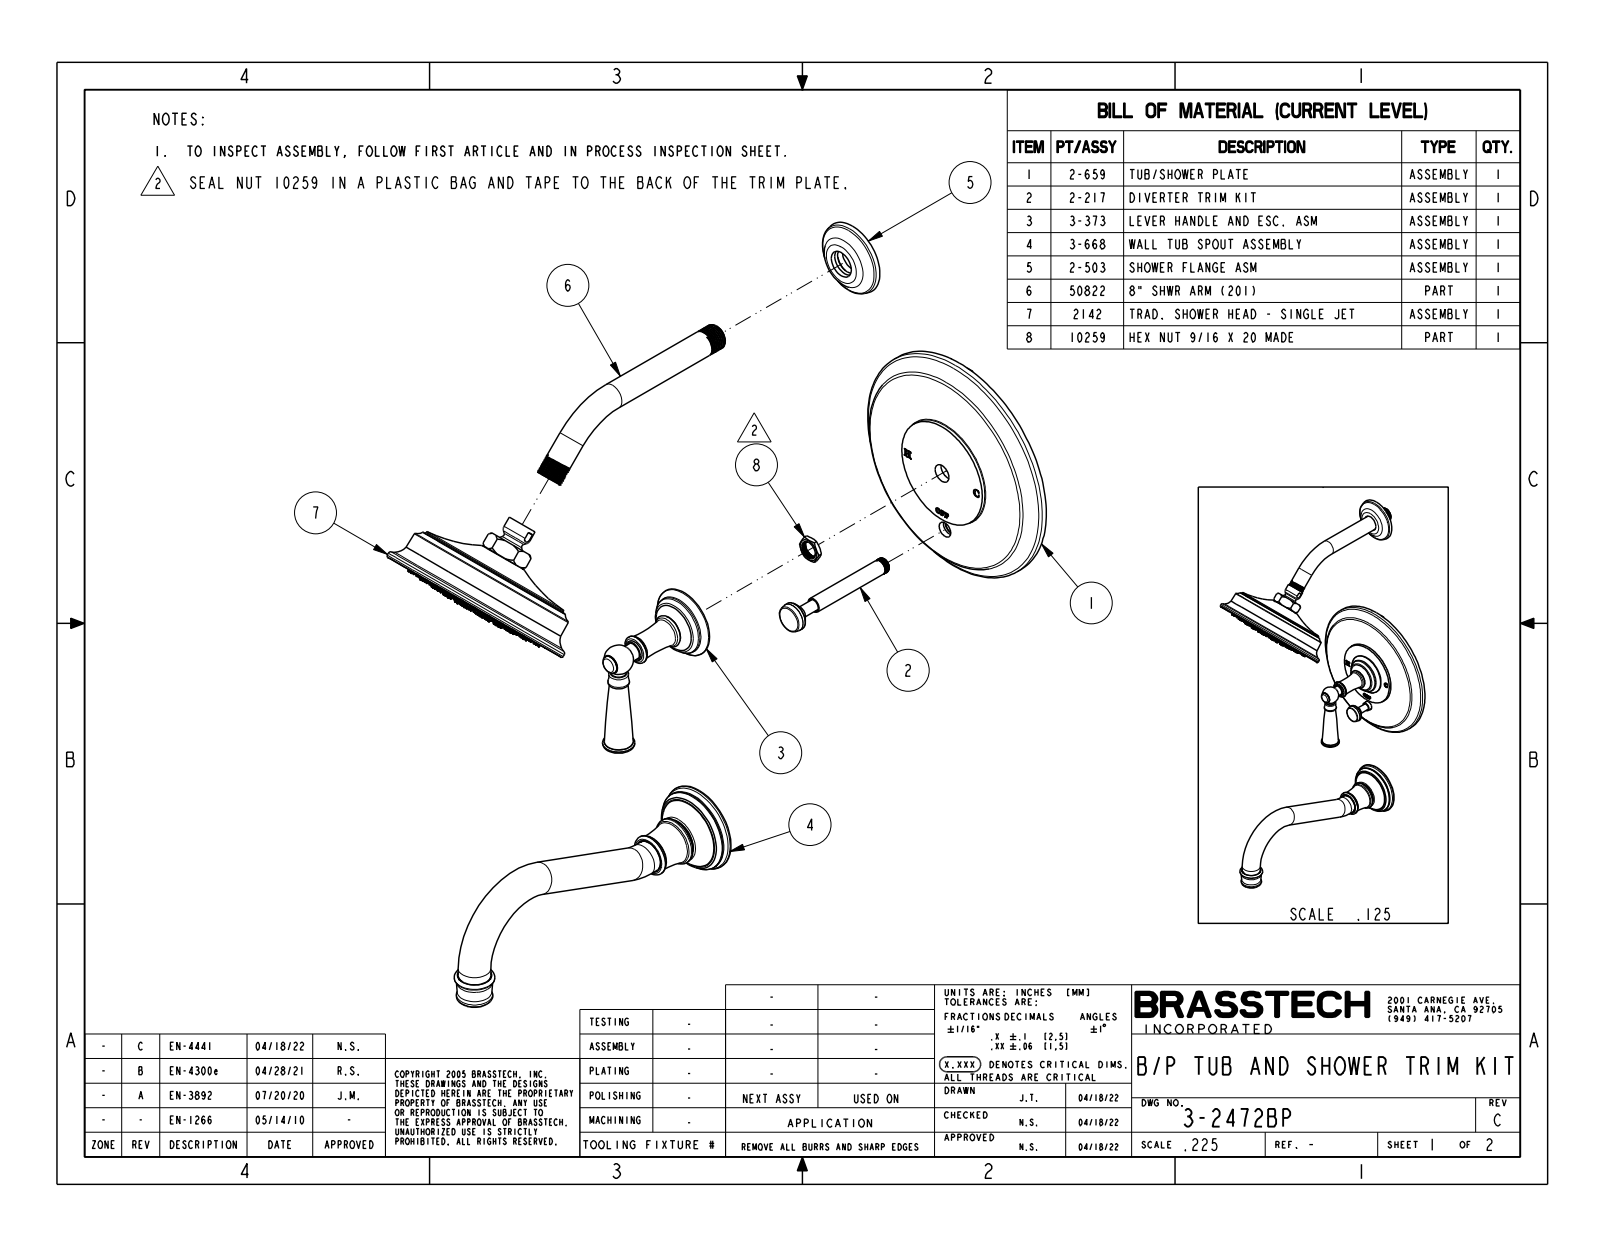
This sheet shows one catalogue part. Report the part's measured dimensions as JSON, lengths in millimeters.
{"part_name": "3-2472BP", "step_written_by": "CREO PARAMETRIC BY PTC INC, 2018400 (CONFIG_CONTROL_DESIGN)", "units": "millimeters", "bodies": {"solids": 3, "faces": 1315, "planar": 279, "cylindrical": 246, "other": 790}, "overall_size": [526.5, 271.6, 190.5], "volume_mm3": 1369000, "surface_area_mm2": 186500, "round_holes": [[1.3, 90], [5.6, 1], [15.3, 1], [134, 1]], "round_bosses_or_shafts": [[25.4, 3], [22.9, 2], [20.7, 2], [190.5, 1], [157.5, 1], [132.6, 1], [122.7, 1], [38.1, 1]], "face_to_face_distances": [15.9, 19.1, 3.2, 12.2, 3.7, 6.9, 25.8, 48.2, 36, 32.3], "hole_center_spacings": [57.7, 12.2, 46.7, 24.2, 46.7, 35.8, 56.9, 66.1]}
